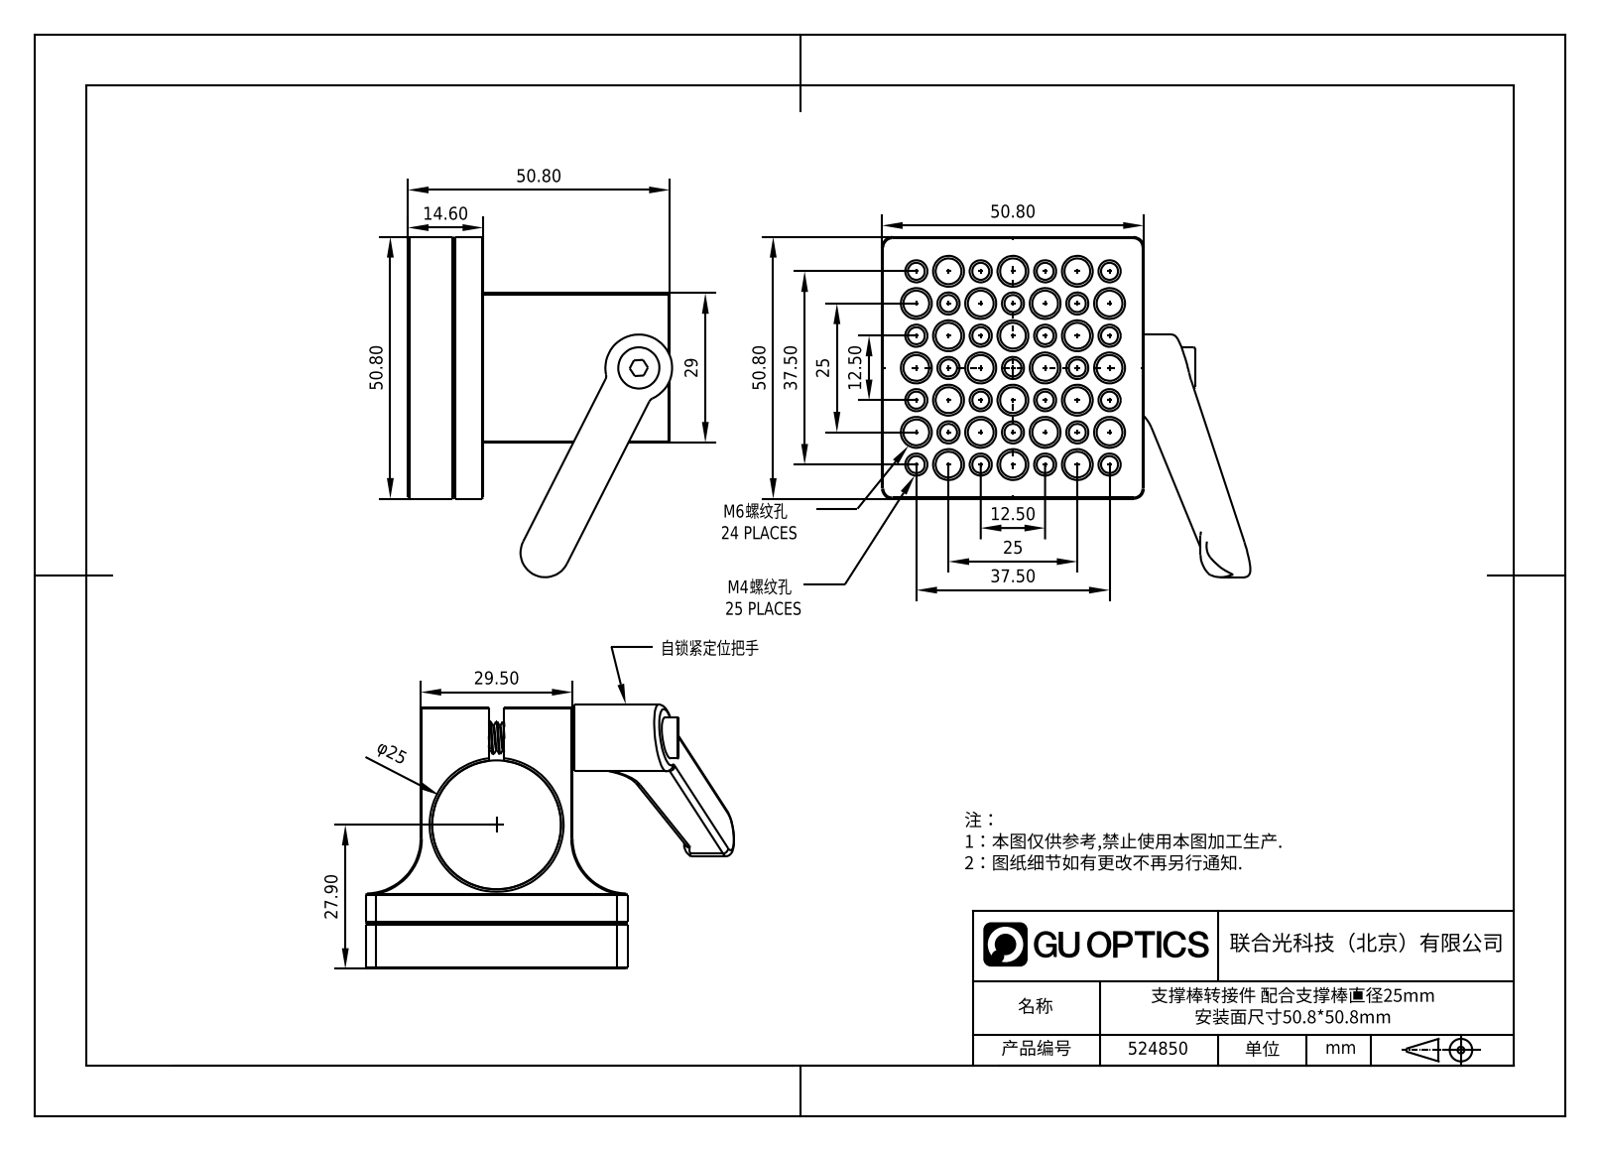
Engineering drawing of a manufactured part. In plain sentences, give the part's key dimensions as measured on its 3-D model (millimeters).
The part is named "1.4.3.26-ZGZ-1.0-JK; 30.1.圆柱头内六角不锈钢螺丝_30.1.118-M4*10; 锁紧定位把手; 接杆安装夹块安装板，零部件，A_1.4.3.26.2，1.0英寸接杆安装夹块安装板，零部件，A (+1 more)". Its 3-D file was written by "SolidWorks 2021 (CONFIG_CONTROL_DESIGN)". It is 8 solids with 604 faces: 116 planar, 196 cylindrical and 292 other. Overall it measures 71.48 by 66 by 51.28 millimeters. Its volume is 54 026 cubic millimeters and its surface area 28 207 square millimeters. Round holes: 25 of diameter 3.3, 25 of diameter 5, 4 of diameter 4.5, 4 of diameter 7.8, 1 of diameter 6.6, 1 of diameter 10.5, 1 of diameter 25. Round bosses or shafts: 4 of diameter 7.2, 4 of diameter 4, 1 of diameter 12.95, 1 of diameter 9.91, 1 of diameter 8, 1 of diameter 6.35, 1 of diameter 3.81. Partial cylindrical surfaces (rounded edges, fillets, slot ends): 4 of radius 1.02, 4 of radius 2, 2 of radius 1.27, 2 of radius 10.65, 1 of radius 0.38, 1 of radius 4.76, 1 of radius 6.35. The main face-to-face distances are 8.89, 50.8, 10.65, 40.15, 10.9, 39.9, 14.61, 5.72, 50.81, 41.92. The hole center spacings are 13.98, 12.5, 31.25, 6.25, 22.53, 19.76, 17.68, 18.75.
